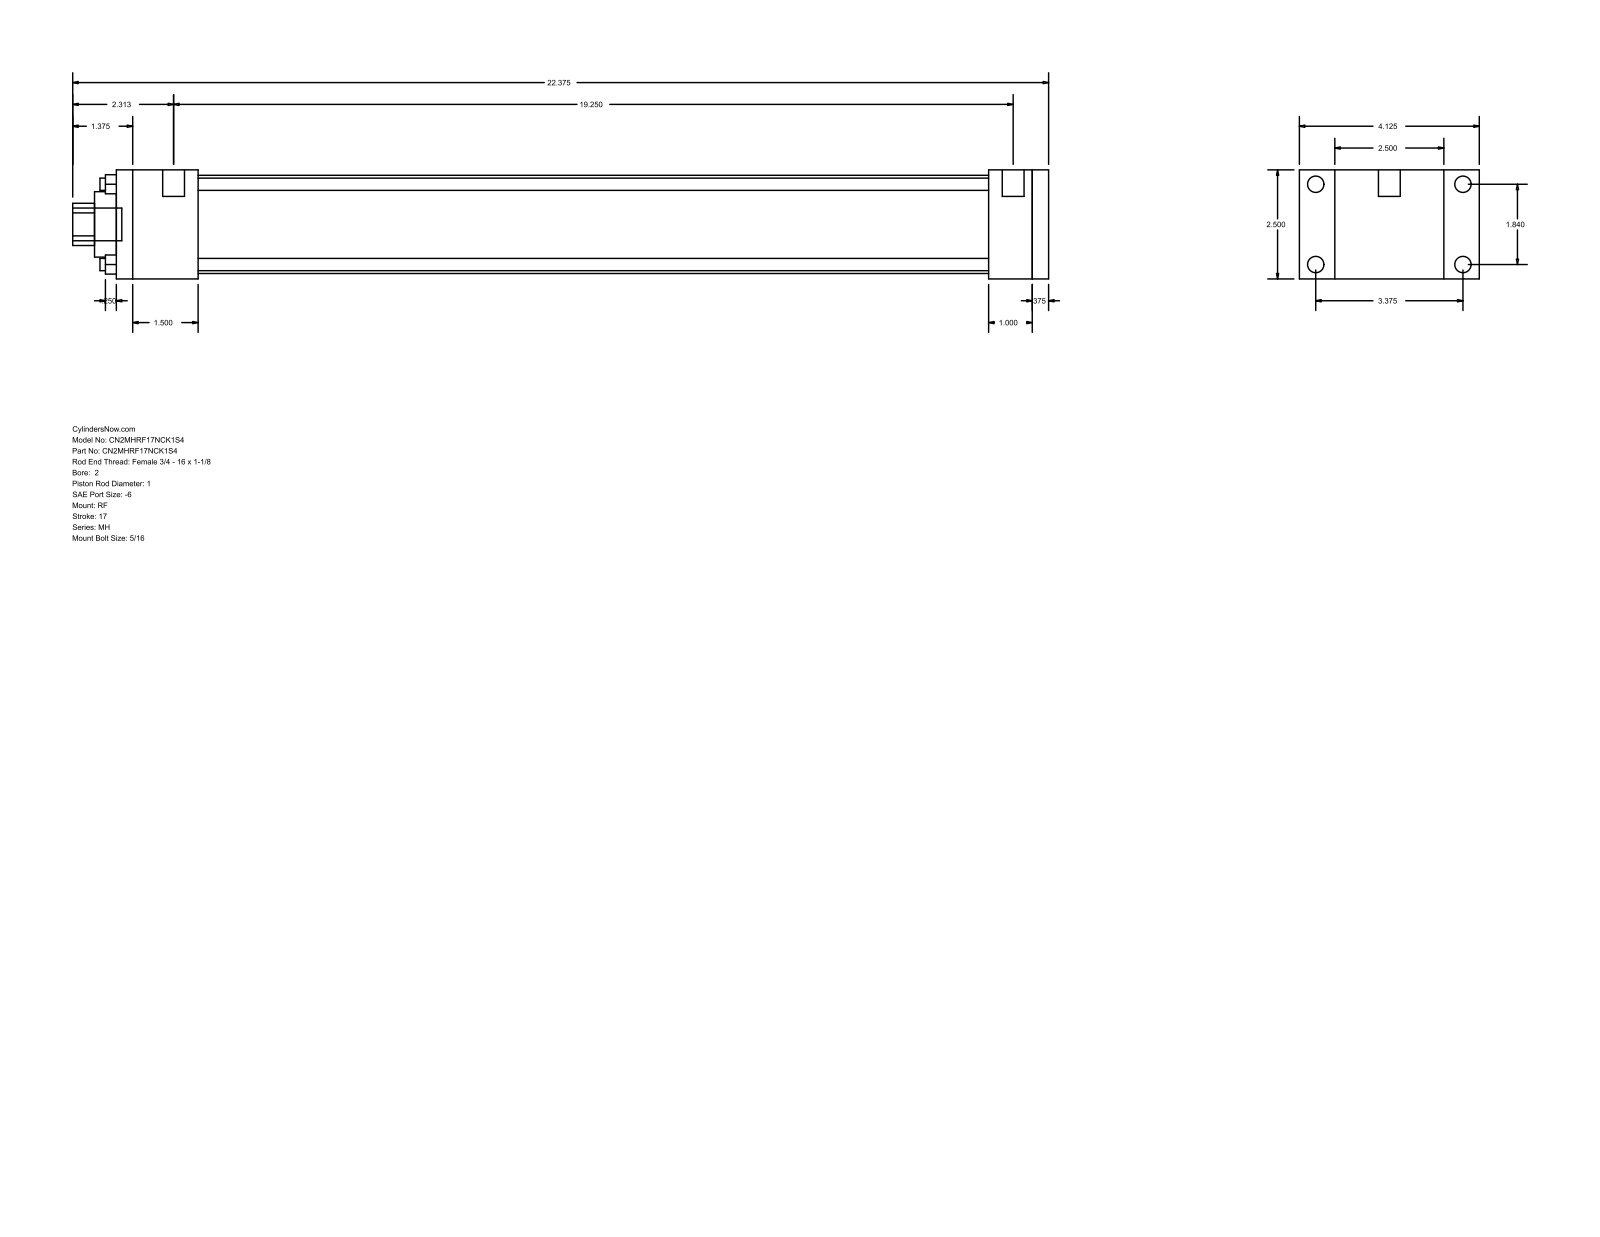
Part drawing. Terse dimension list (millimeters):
name: MH_RF__0200_1
written by: GSSL Pune (CONFIG_CONTROL_DESIGN)
unit: mm
bodies: 0 solids, 92 faces (64 planar, 28 cylindrical, 0 other)
size: 568.33 × 104.78 × 63.5
holes: 4× ⌀7.14, 1× ⌀25.4, 1× ⌀38.1, 1× ⌀57.15
bosses: 4× ⌀9.53, 4× ⌀5.56, 2× ⌀12.7, 1× ⌀19.05
rounds: 1× R12.29
face distances: 63.5, 542.93, 533.4, 9.53, 20.64, 25.4, 47.63, 508, 460.37, 485.77
hole spacings: 33.05, 46.74, 66.1
